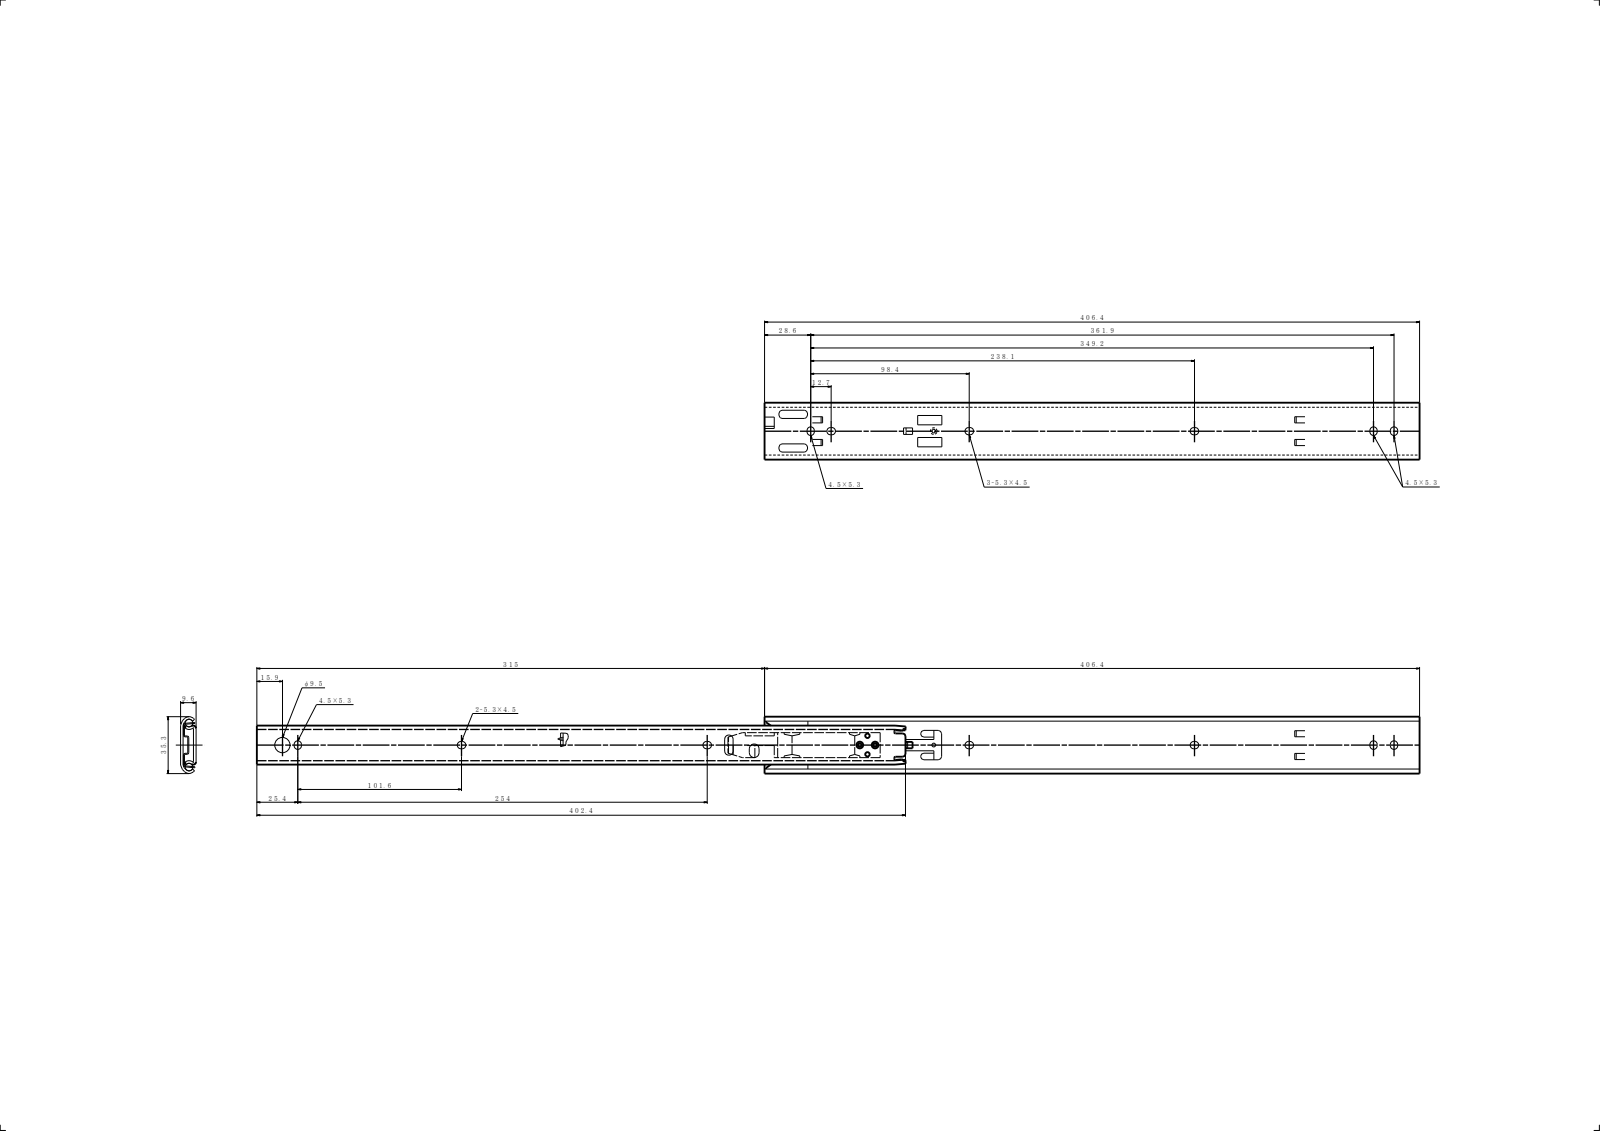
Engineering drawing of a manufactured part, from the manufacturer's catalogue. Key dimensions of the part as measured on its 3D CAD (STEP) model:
Part name (STEP PRODUCT): PN84 ol; PN235リードイン; IM 3525-16; PN102リベット (+3 more)
STEP written by: SolidWorks 2019 (CONFIG_CONTROL_DESIGN)
Units: millimetres
Bodies: 8 solids, 351 faces (170 planar, 172 cylindrical, 9 other)
Overall size (bounding box): 721.4 × 35.3 × 9.6
Volume: 52 731 mm³ · Surface area: 71 781 mm²
Round holes (diameter × count): ⌀2.4 ×3, ⌀2.6 ×3, ⌀4.2 ×3, ⌀2.8 ×2, ⌀9.5 ×1
Round bosses / shafts (diameter × count): ⌀2.3 ×3, ⌀4.6 ×2, ⌀2.7 ×2
Partial cylindrical surfaces — rounded edges, fillets, slot ends (radius × count): R2.25 ×22, R0.3 ×10, R3 ×10, R1.5 ×9, R0.5 ×6, R0.8 ×6, R2 ×6, R1.6 ×5
Main face-to-face distances: 1.6, 8, 6.4, 9.6, 0.8, 1.3, 4.67, 3.07, 5.1, 2.9
Hole centre spacings: 7.5, 41.56, 363, 9.5, 11.6, 36.4, 45.9, 358.2
